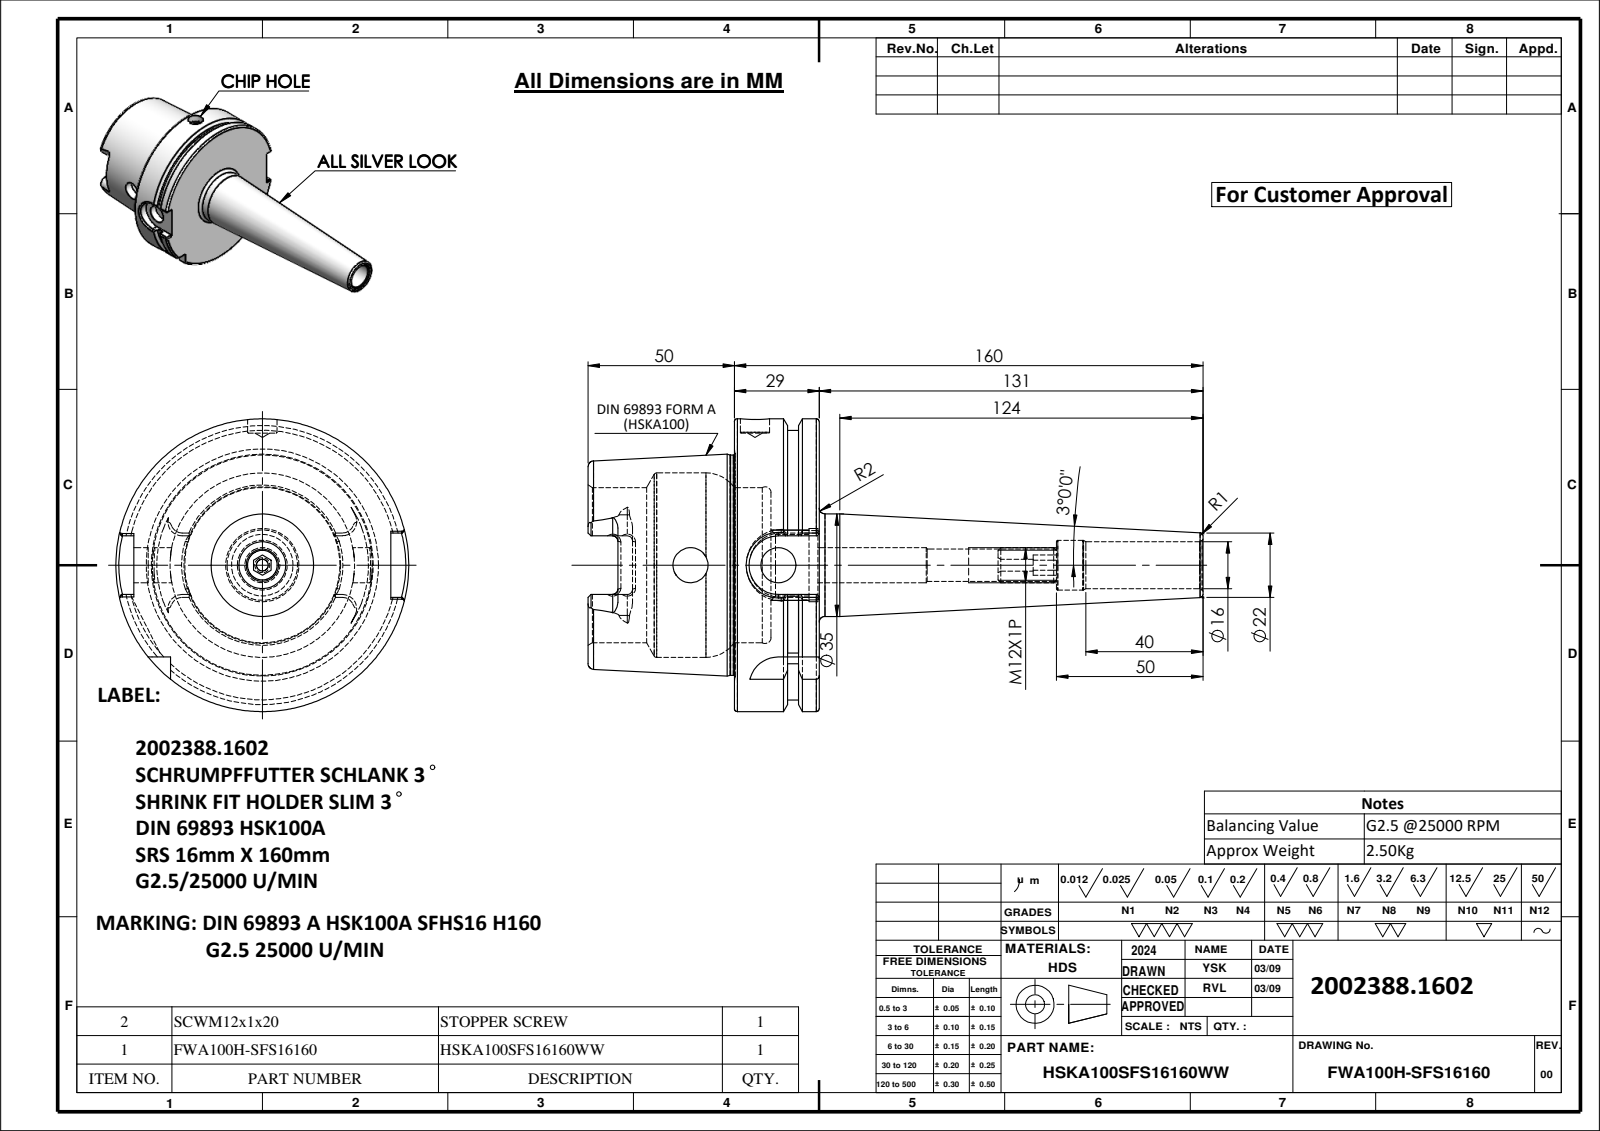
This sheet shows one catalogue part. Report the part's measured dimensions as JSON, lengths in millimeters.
{"part_name": "SCWM12X1P; HSKA100SFS16160WW; FWA100H-SFS16160", "step_written_by": "SolidWorks 2024 (CONFIG_CONTROL_DESIGN)", "units": "millimeters", "bodies": {"solids": 2, "faces": 205, "planar": 61, "cylindrical": 58, "other": 86}, "overall_size": [210, 100, 100], "volume_mm3": 324081, "surface_area_mm2": 67583, "round_holes": [[12, 3], [4, 1], [10, 1], [11, 1], [16, 1], [17, 1], [21, 1], [25, 1], [53, 1], [63, 1]], "round_bosses_or_shafts": [[100, 1], [92, 1], [75.16, 1], [35, 1]], "partial_cylinders_radius": [[1.8, 6], [4.88, 4], [10, 2], [11, 1]], "face_to_face_distances": [28.95, 12.5, 16.45, 50, 62.5, 78.95, 71.88, 21.88, 9.38, 7.07], "hole_center_spacings": [30]}
